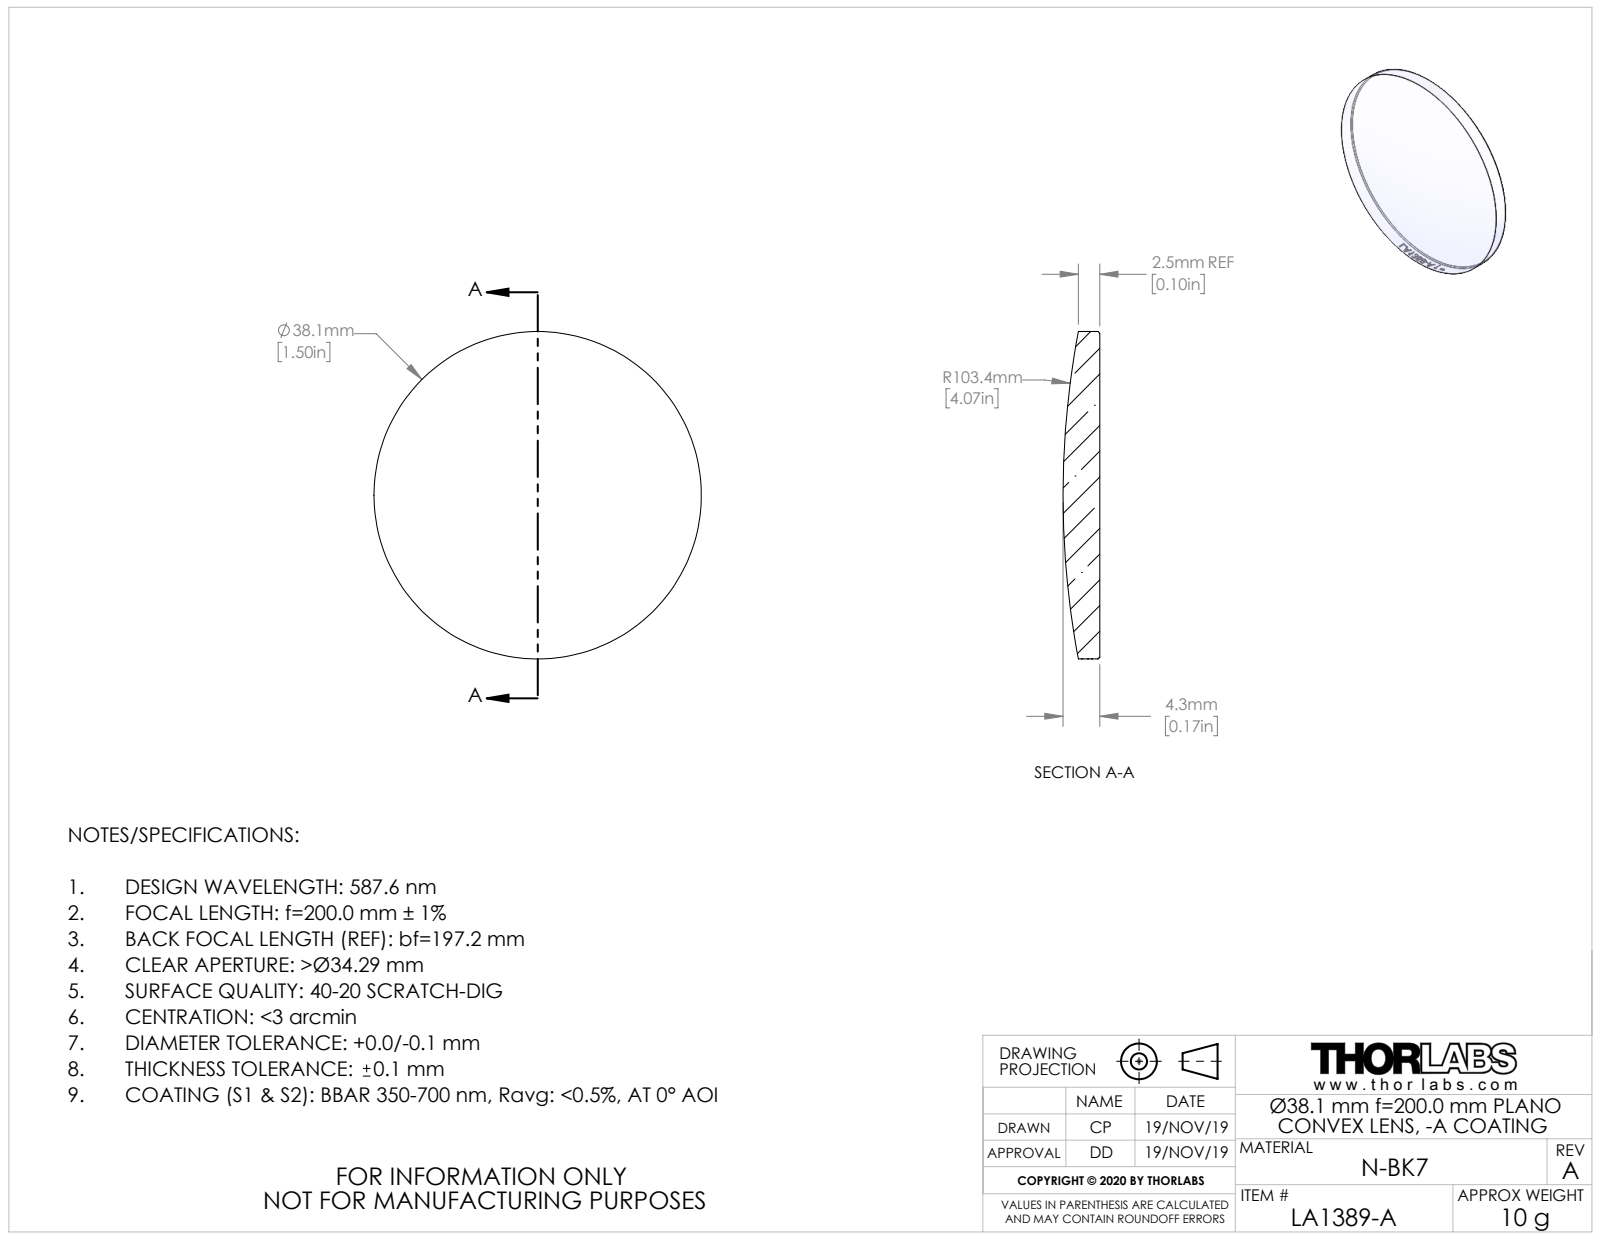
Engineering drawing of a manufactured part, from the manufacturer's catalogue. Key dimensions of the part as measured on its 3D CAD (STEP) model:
Part name (STEP PRODUCT): TTN200714-E0W
STEP written by: SolidWorks 2018 (CONFIG_CONTROL_DESIGN)
Units: millimetres
Bodies: 1 solid, 24 faces (1 planar, 19 cylindrical, 4 other)
Overall size (bounding box): 38.1 × 38.1 × 4.27
Volume: 3 859 mm³ · Surface area: 2 575 mm²
Round bosses / shafts (diameter × count): ⌀38.1 ×1
